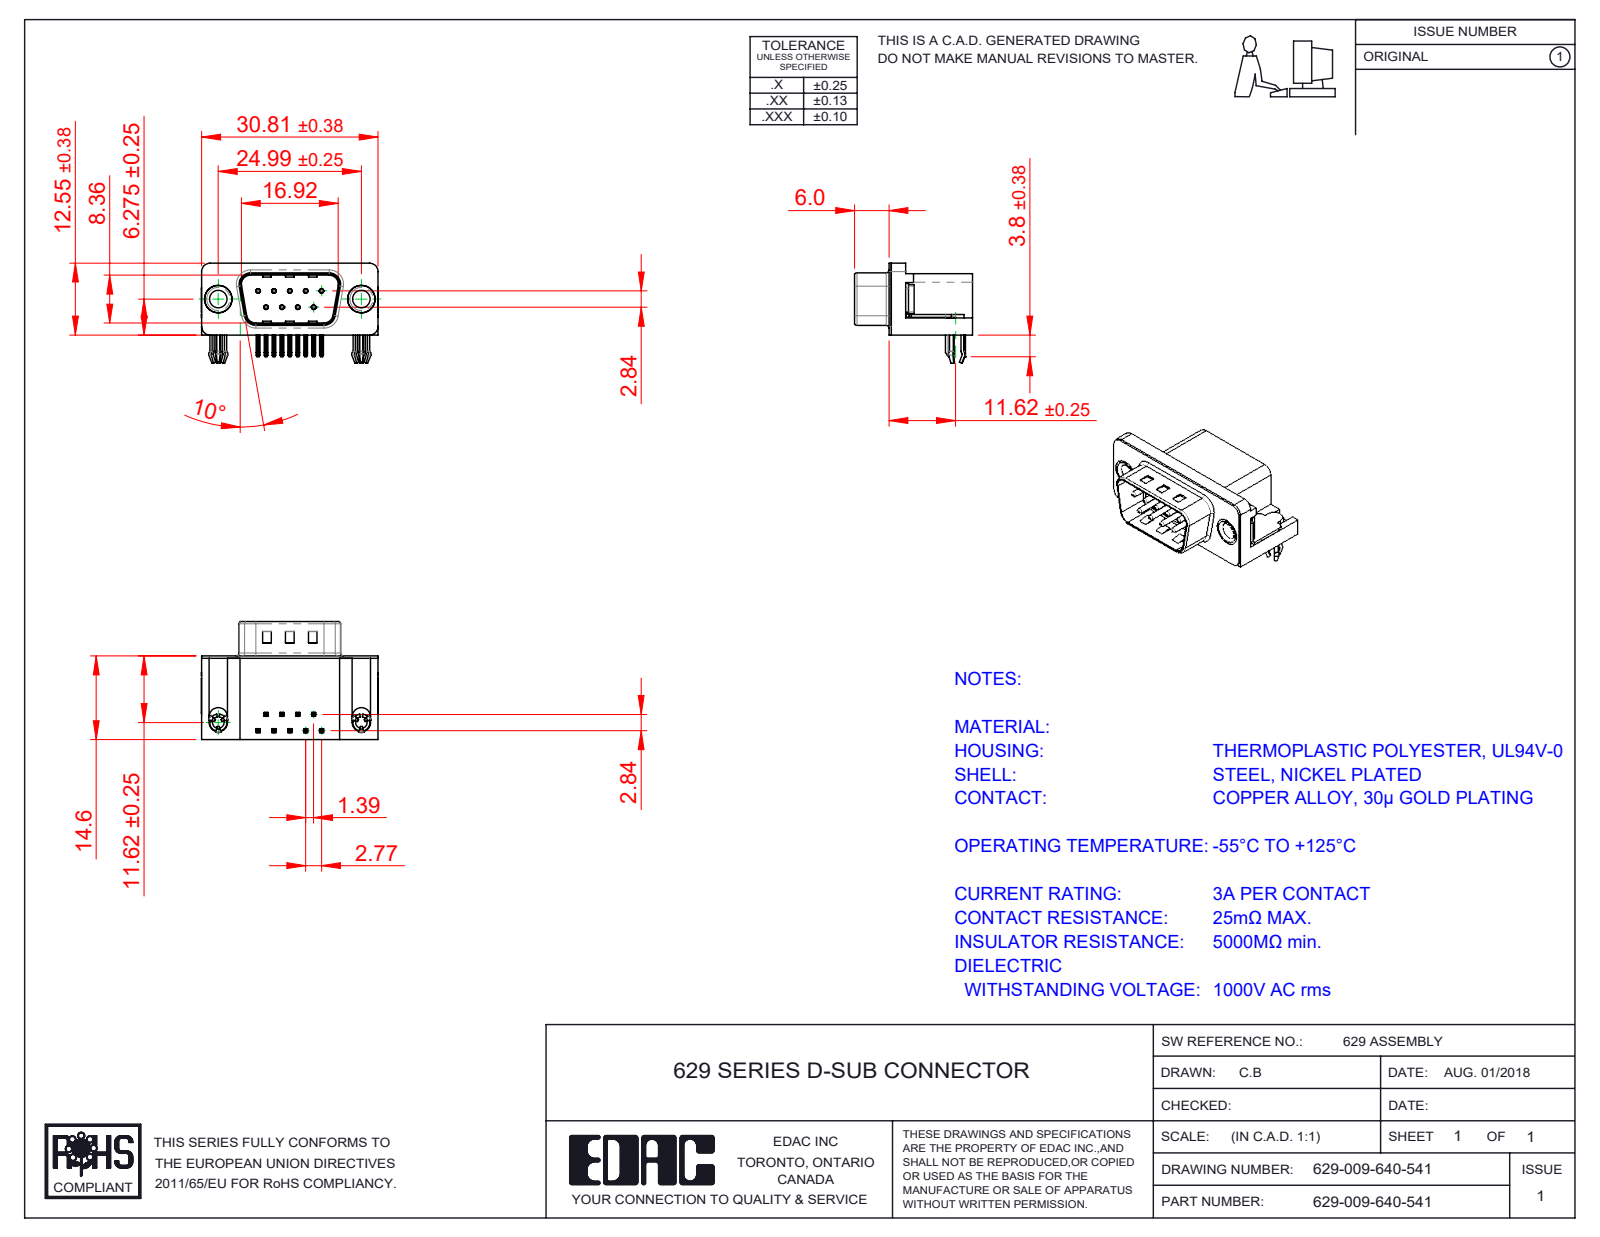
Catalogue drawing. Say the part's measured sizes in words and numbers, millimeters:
The part is named "629 Contact Top; 629 Thru Hole Rivet; 629 3 Prong Board Lock; 629 Housing_09 Socket (+3 more)". Its 3-D file was written by "SolidWorks 2020 (CONFIG_CONTROL_DESIGN)". It is 15 solids with 1053 faces: 609 planar, 303 cylindrical and 141 other. Overall it measures 30.89 by 20.6 by 17.48 millimeters. Its volume is 3 718 cubic millimeters and its surface area 4 796 square millimeters. Round holes: 9 of diameter 0.35, 9 of diameter 0.8, 2 of diameter 2, 2 of diameter 3.05, 2 of diameter 4, 2 of diameter 4.8, 2 of diameter 5. Round bosses or shafts: 9 of diameter 0.75, 2 of diameter 4.9, 2 of diameter 4.75, 2 of diameter 3.85, 2 of diameter 3. Partial cylindrical surfaces (rounded edges, fillets, slot ends): 48 of radius 0.25, 18 of radius 0.12, 16 of radius 1, 9 of radius 0.5, 8 of radius 1.5, 8 of radius 1.6, 4 of radius 0.9, 4 of radius 2. The main face-to-face distances are 0.4, 14.2, 10.35, 14.6, 0.5, 2.9, 11.7, 2.5, 2.1, 6.7. The hole center spacings are 3.16, 2.77, 5.54, 5.03, 5.04, 8.31, 7.48, 7.49.
